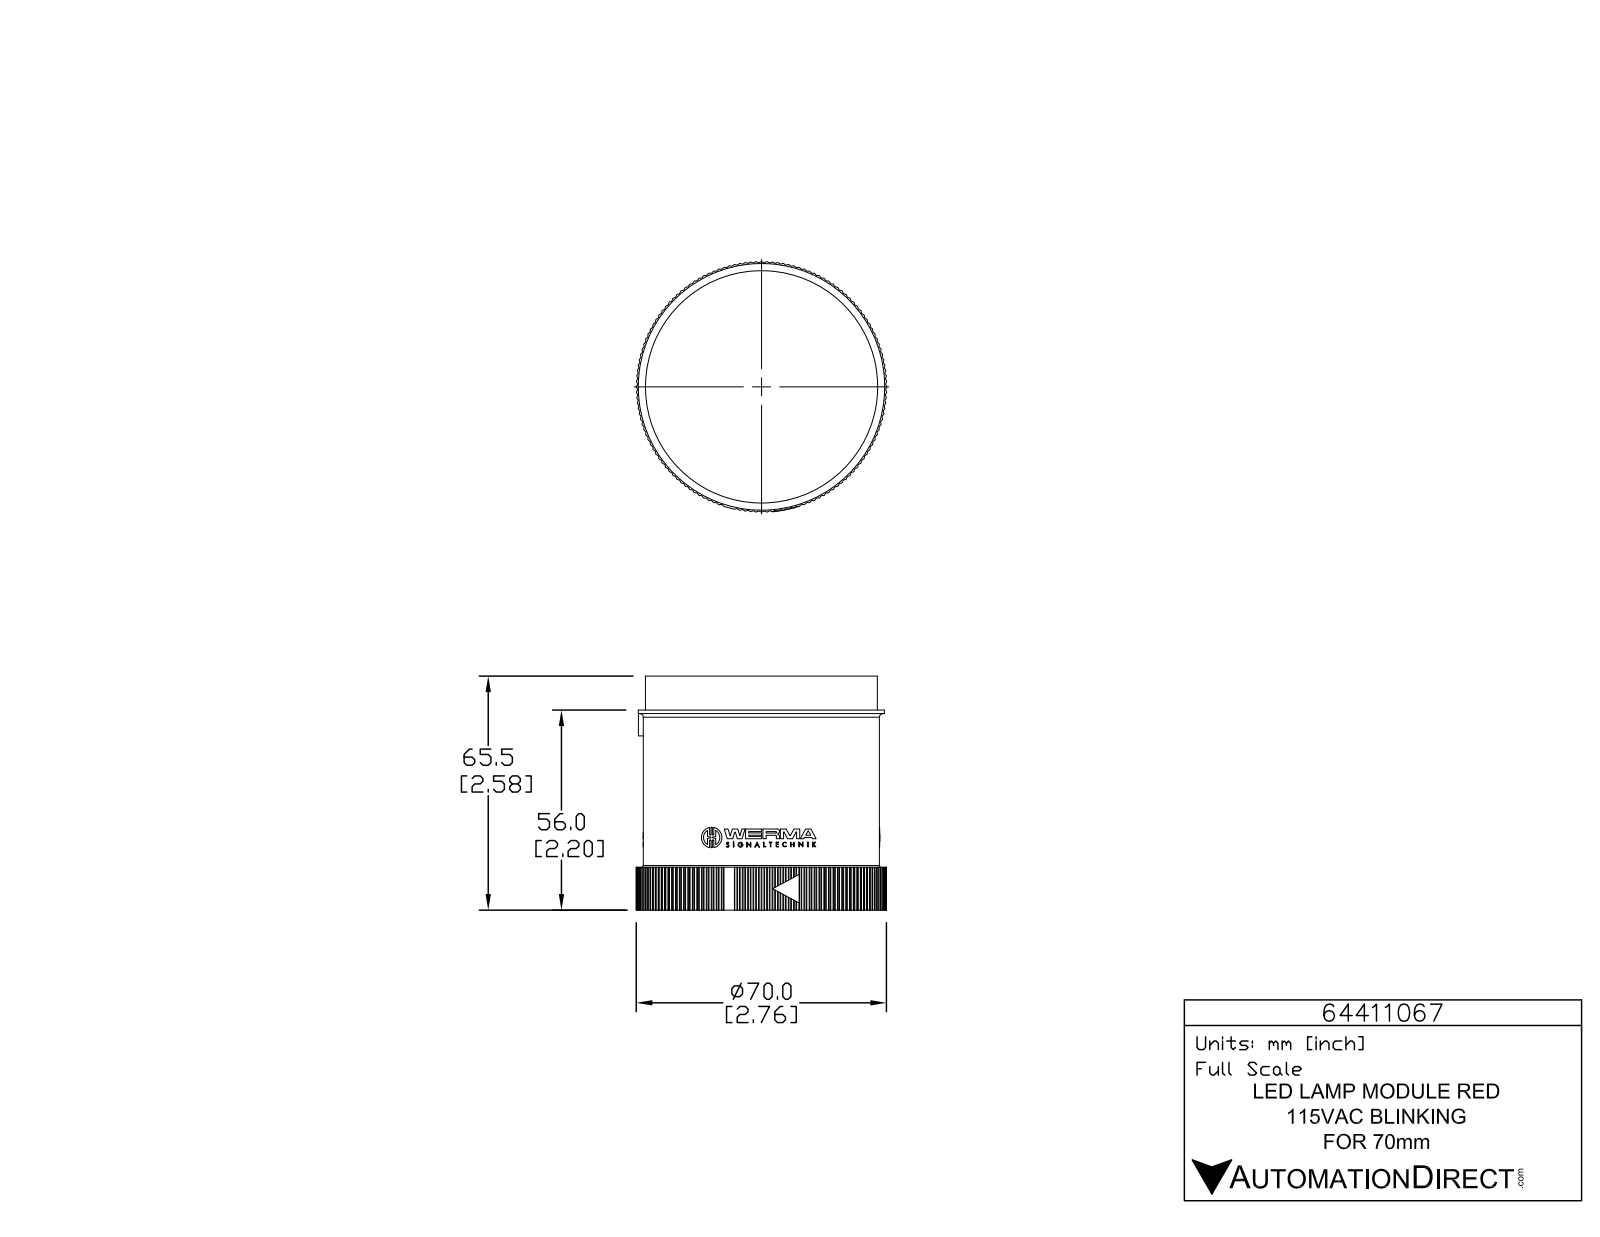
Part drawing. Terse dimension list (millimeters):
name: 64411067
written by: SolidWorks 2015 (AUTOMOTIVE_DESIGN)
unit: mm
bodies: 1 solid, 1400 faces (832 planar, 563 cylindrical, 5 other)
size: 70.2 × 70.2 × 65.5
volume: 197 000 mm³; area: 24 180 mm²
holes: 3× ⌀1, 1× ⌀65.4
bosses: 3× ⌀5.7, 3× ⌀1.4, 1× ⌀69, 1× ⌀66.2, 1× ⌀65
rounds: 285× R0.2, 6× R0.2, 6× R0.2, 6× R0.2, 6× R3.3, 3× R0.1, 3× R0.1, 3× R0.2
face distances: 55.9, 62.3, 9.6, 65.5, 56, 46.4, 9.5, 62.3, 12, 2.4
